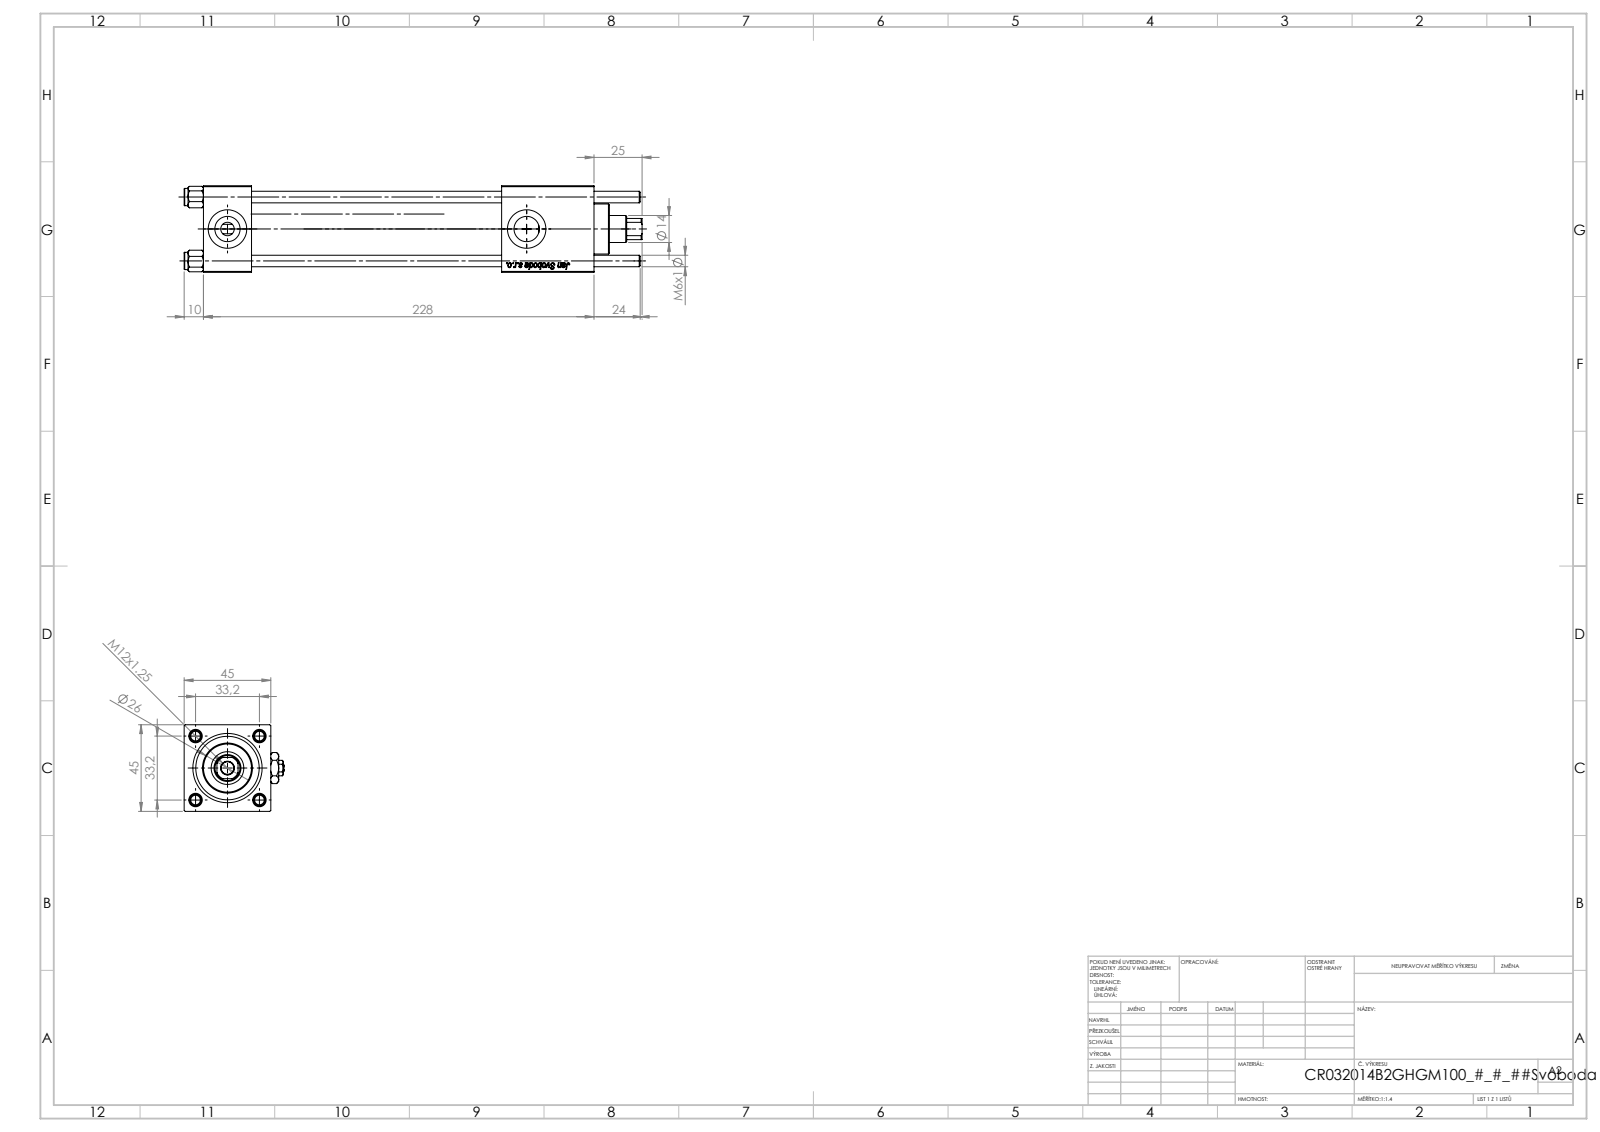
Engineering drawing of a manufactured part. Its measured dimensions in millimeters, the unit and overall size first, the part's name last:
Units: millimetres
Overall size (bounding box): 238 × 52 × 45
Round holes (diameter × count): ⌀6 ×4, ⌀7 ×2, ⌀13.16 ×2, ⌀20 ×2, ⌀6.5 ×1, ⌀14 ×1, ⌀17 ×1, ⌀24 ×1, ⌀32 ×1, ⌀33 ×1
Round bosses / shafts (diameter × count): ⌀9 ×4, ⌀38 ×1, ⌀26 ×1
Partial cylindrical surfaces — rounded edges, fillets, slot ends (radius × count): R6.5 ×1
Main face-to-face distances: 45, 25, 203, 178, 155, 130, 48, 174.3, 149.3, 19.3
Hole centre spacings: 23.48, 33.2, 46.95, 155.5
Volume: 245 275 mm³ · Surface area: 100 794 mm²
Bodies: 12 solids, 1208 faces (454 planar, 84 cylindrical, 670 other)
Part name (STEP PRODUCT): V215CR_B_TYCINKA; V215_VC_A; Zatka_pro_OIL_PORT; V215CR_B-1 (+2 more)
STEP written by: SolidWorks 2019 (CONFIG_CONTROL_DESIGN)
